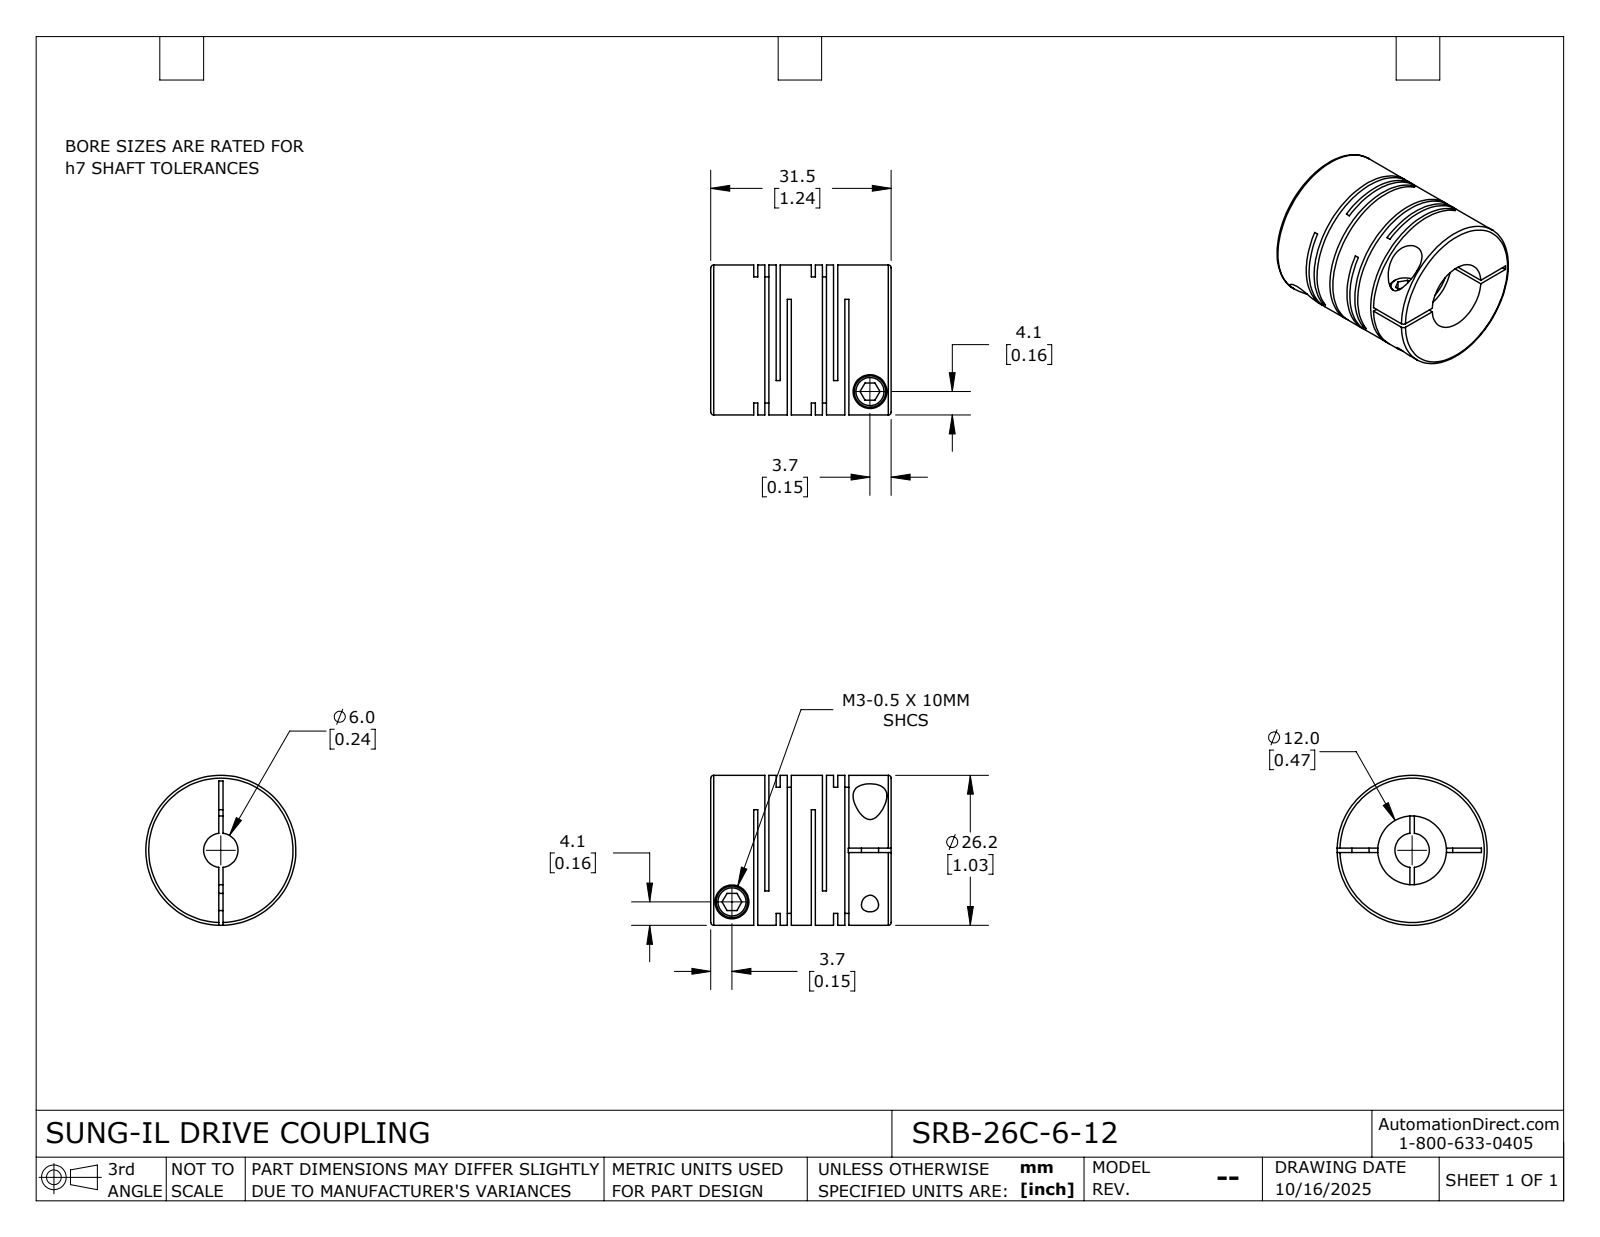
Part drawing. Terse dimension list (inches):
name: SRB-26C-6-12
written by: SolidWorks 2024 (CONFIG_CONTROL_DESIGN)
unit: in
bodies: 1 solid, 115 faces (60 planar, 42 cylindrical, 13 other)
size: 1.24 × 1.031 × 1.031
volume: 0.712 in³; area: 16 in²
holes: 2× ⌀0.118, 2× ⌀0.232, 1× ⌀0.236, 1× ⌀0.472
bosses: 2× ⌀0.217, 1× ⌀1.031
face distances: 0.077, 0.396, 0.028, 0.154, 0.319, 0.472, 0.049, 0.105, 0.368, 0.549
